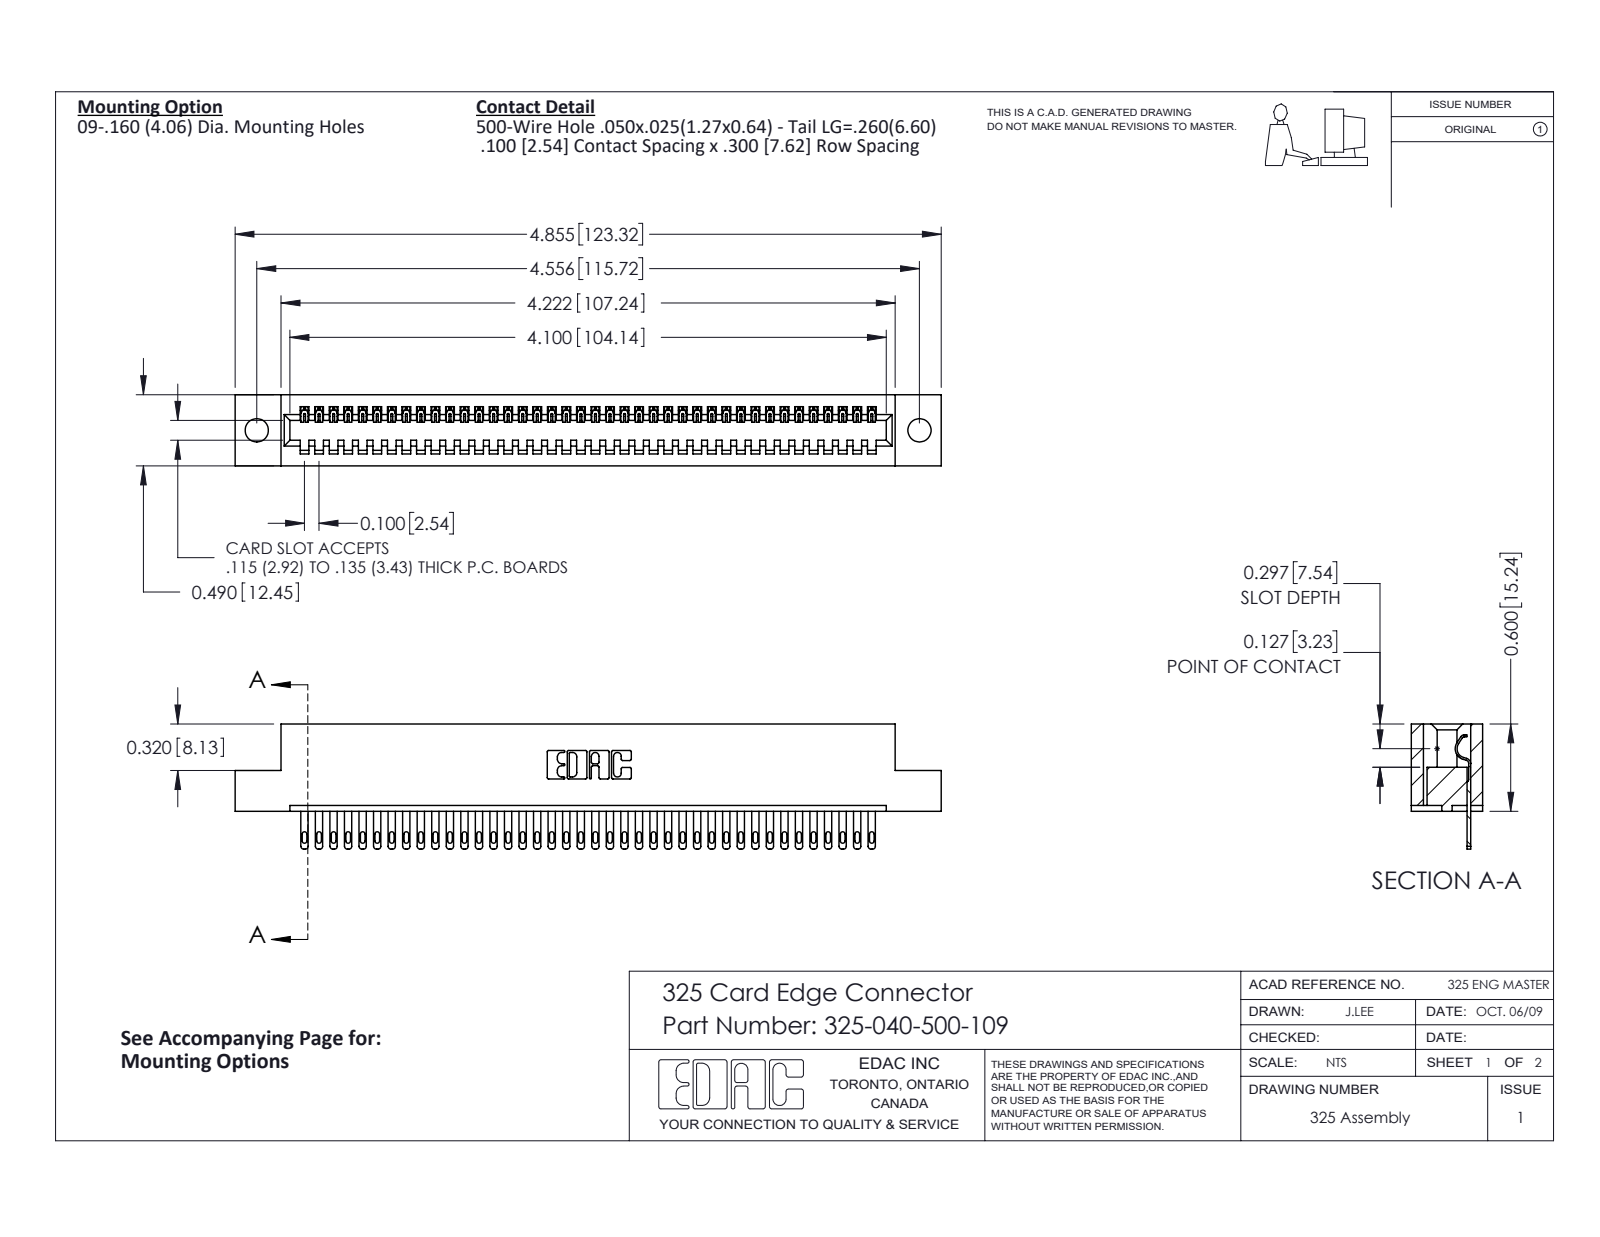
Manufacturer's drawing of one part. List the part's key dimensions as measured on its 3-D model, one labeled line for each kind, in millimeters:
Part name (STEP PRODUCT): 325-292-001_325-293-100; 325 Part_.160 TH; 325-040-500-109
STEP written by: SolidWorks 2016 (CONFIG_CONTROL_DESIGN)
Units: millimetres
Bodies: 41 solids, 2274 faces (1510 planar, 764 cylindrical, 0 other)
Overall size (bounding box): 123.3 × 21.8 × 12.4
Volume: 15 400 mm³ · Surface area: 16 820 mm²
Round holes (diameter × count): ⌀4.1 ×2
Partial cylindrical surfaces — rounded edges, fillets, slot ends (radius × count): R0.2 ×80, R0.4 ×80, R0.5 ×80, R0.3 ×22, R0.2 ×6, R0.8 ×6, R0.7 ×3, R0.4 ×1
Main face-to-face distances: 2.1, 10.3, 12.4, 7.6, 2.7, 9.7, 0.6, 8.3, 14.2, 6.7
Hole centre spacings: 115.7
